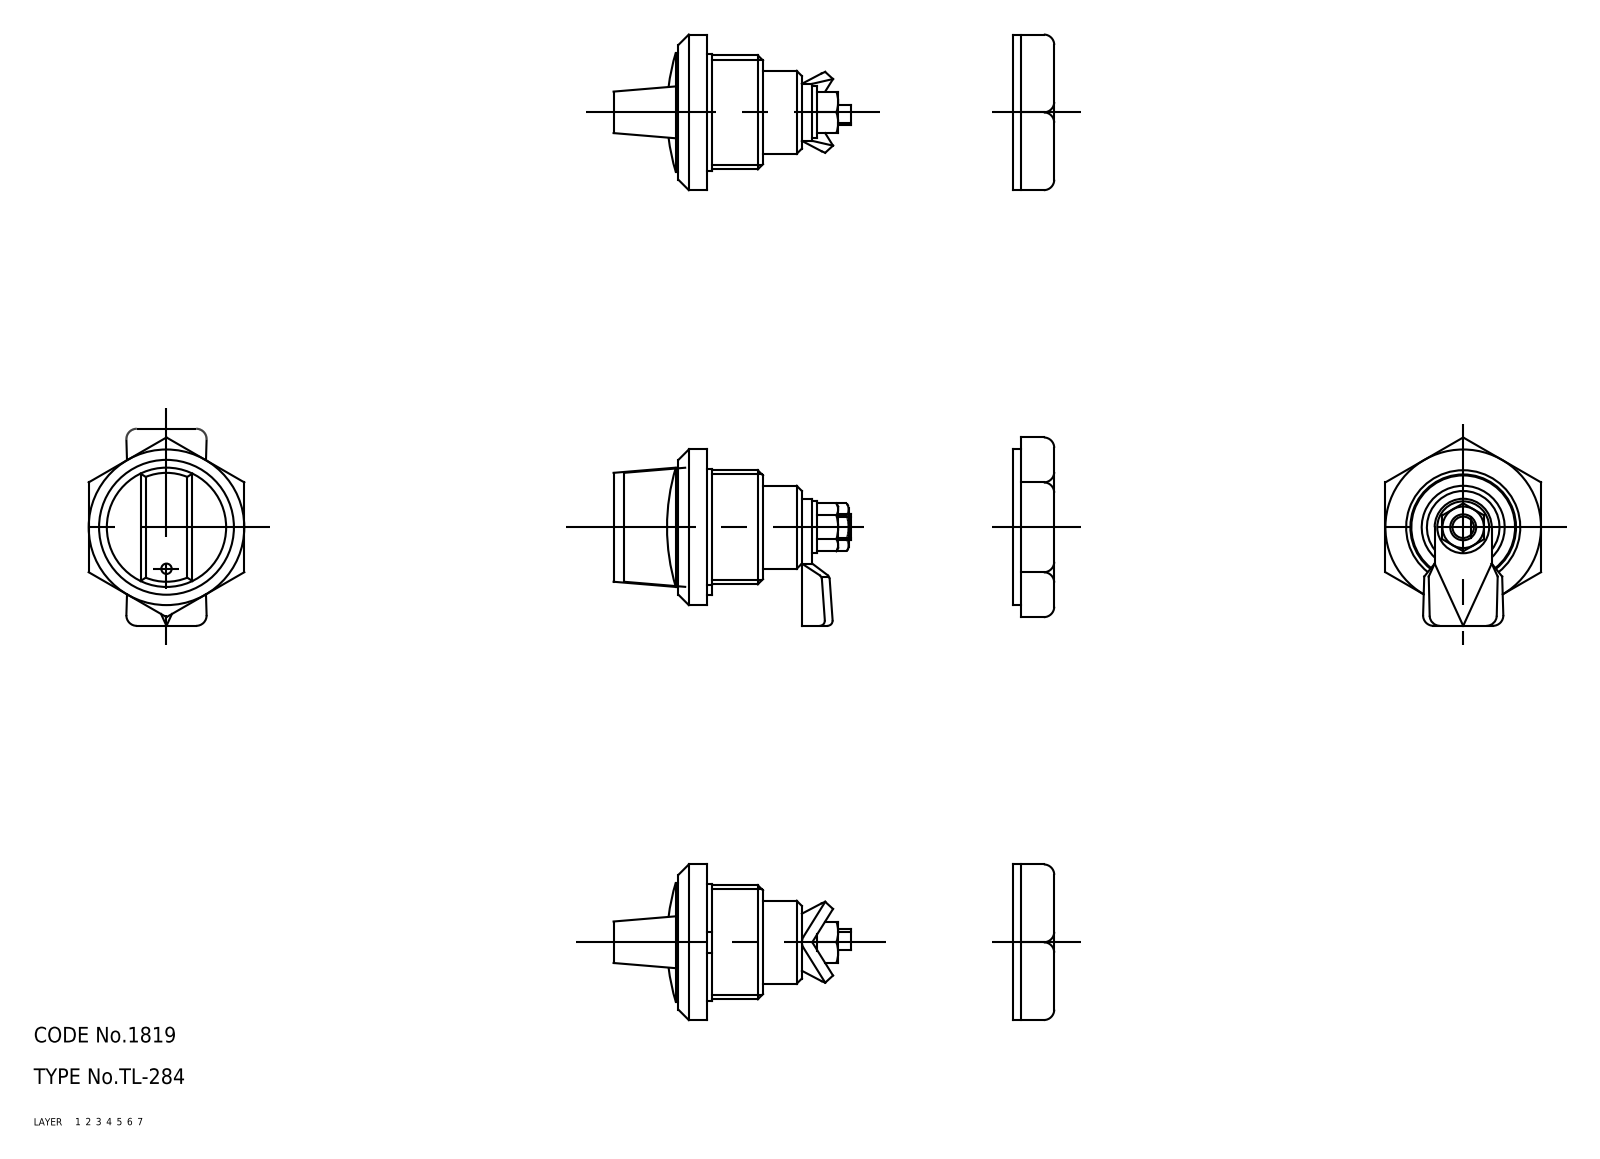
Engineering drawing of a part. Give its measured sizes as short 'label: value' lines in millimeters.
name: 67115352; 67115365; 67115378; 67115391 (+1 more)
written by: CADfix (AUTOMOTIVE_DESIGN)
unit: mm
bodies: 5 solids, 115 faces (0 planar, 0 cylindrical, 115 other)
size: 45.8 × 36.32 × 30
volume: 15 183 mm³; area: 9 125 mm²
